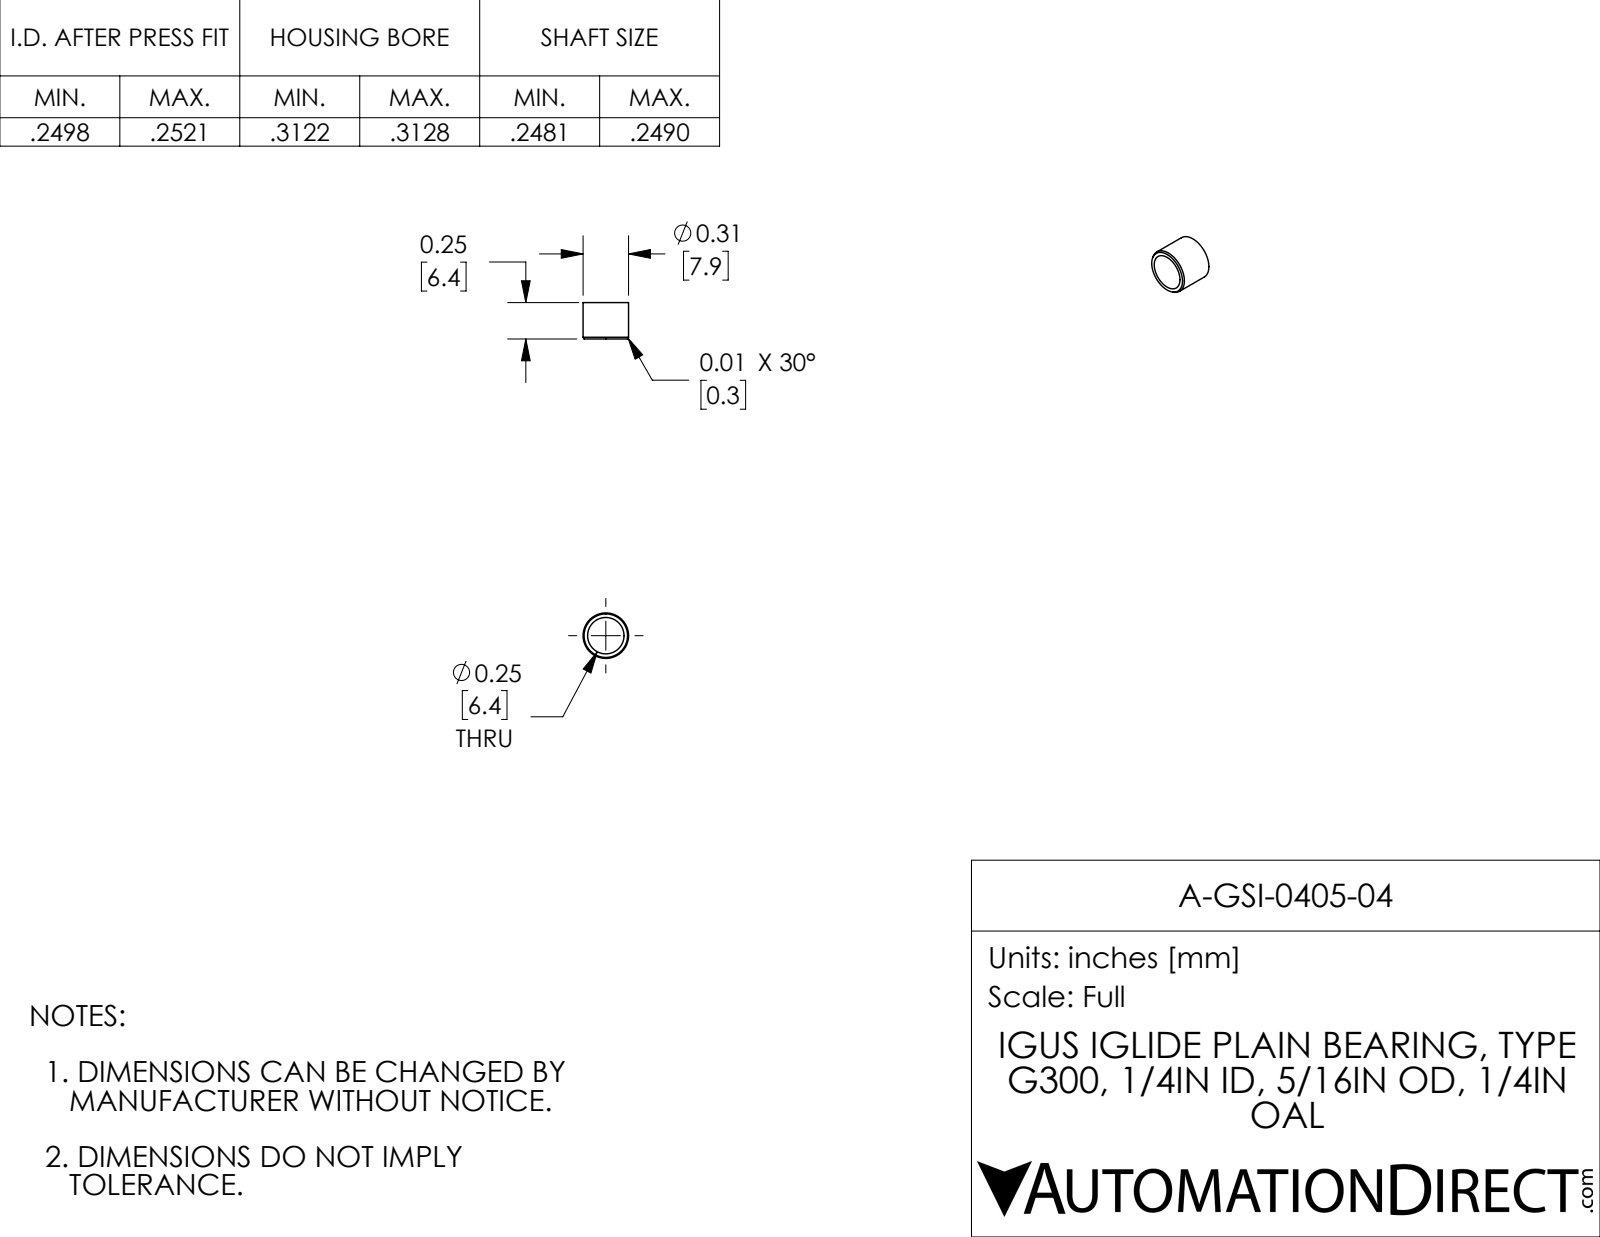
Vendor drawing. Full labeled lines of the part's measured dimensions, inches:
Part name (STEP PRODUCT): A-GSI-0405-04
STEP written by: SolidWorks 2017 (AUTOMOTIVE_DESIGN)
Units: inches
Bodies: 1 solid, 10 faces (2 planar, 4 cylindrical, 4 other)
Overall size (bounding box): 0.313 × 0.313 × 0.25
Volume: 0.007 in³ · Surface area: 0.486 in²
Round holes (diameter × count): ⌀0.25 ×1
Round bosses / shafts (diameter × count): ⌀0.313 ×1
Main face-to-face distances: 0.25
